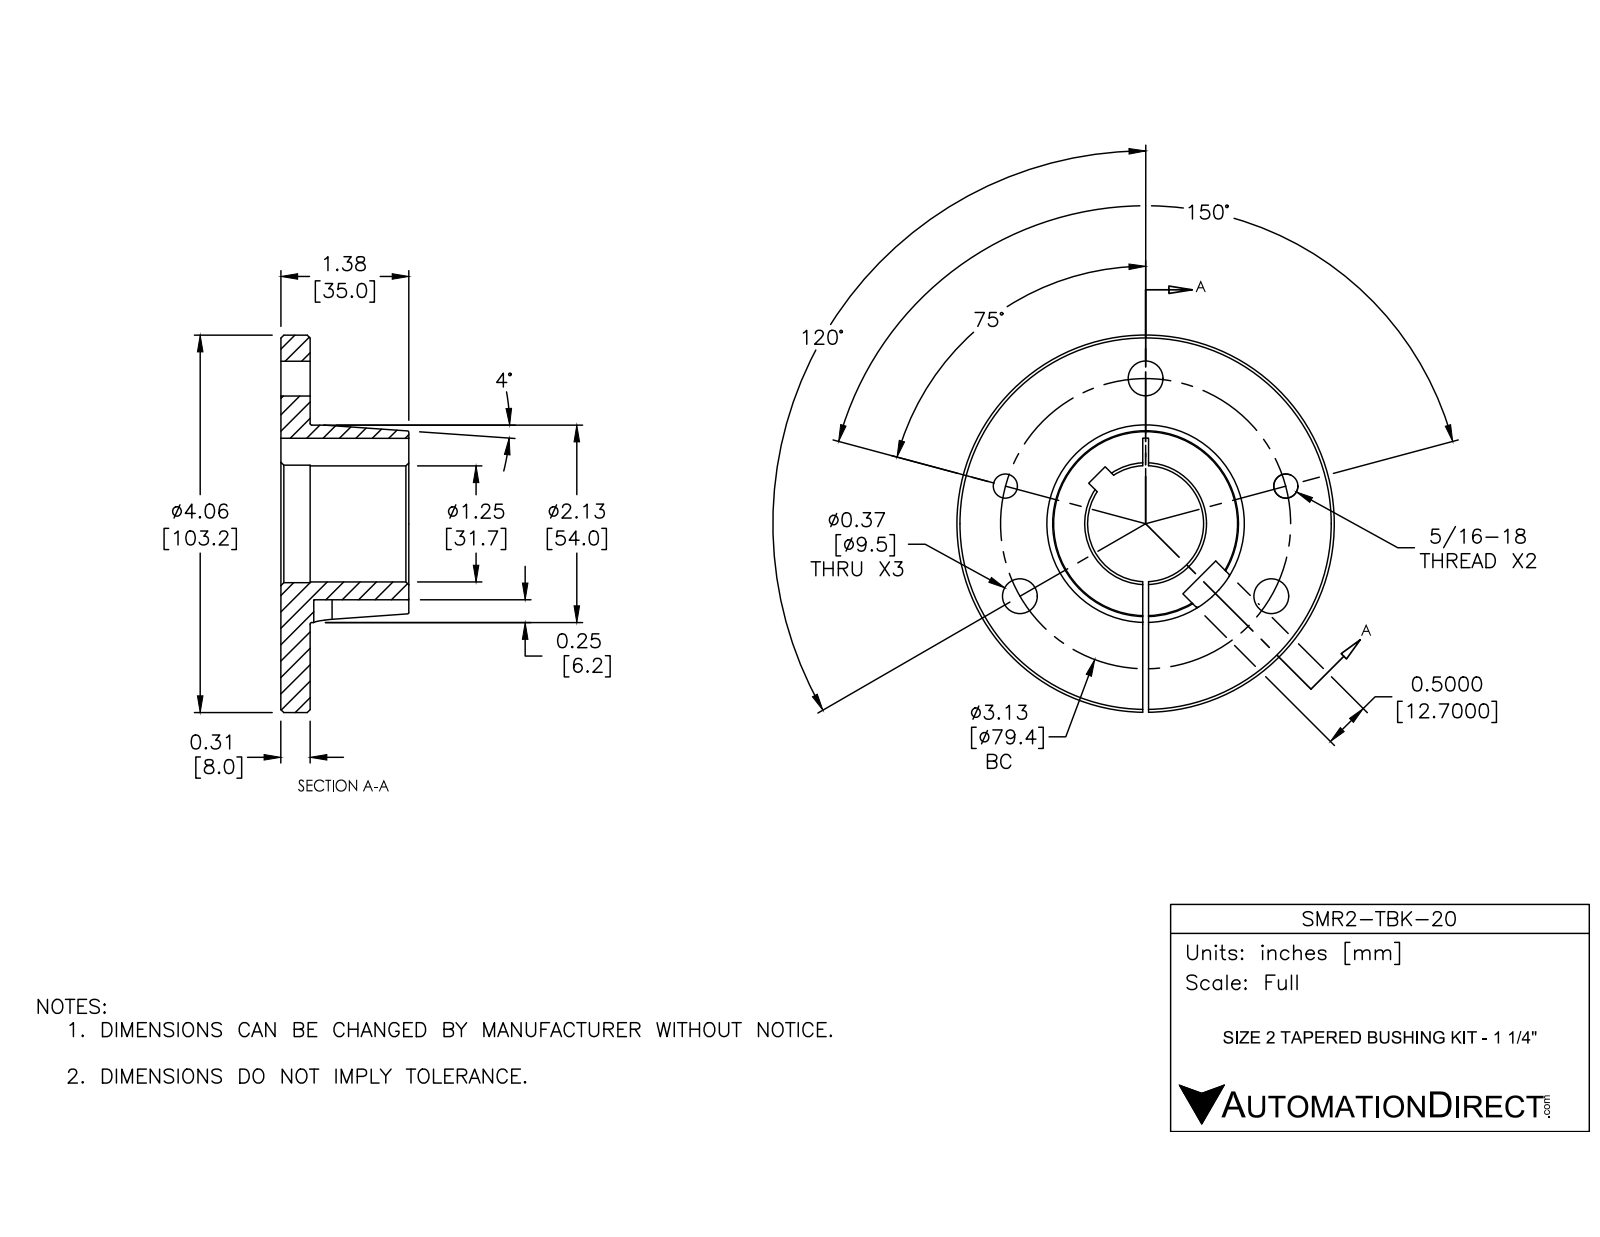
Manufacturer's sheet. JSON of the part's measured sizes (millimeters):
{"part_name": "SMR2-TBK-20", "step_written_by": "SolidWorks 2016 (AUTOMOTIVE_DESIGN)", "units": "millimeters", "bodies": {"solids": 1, "faces": 124, "planar": 18, "cylindrical": 79, "other": 27}, "overall_size": [103.2, 103.2, 35], "volume_mm3": 91490, "surface_area_mm2": 27550, "round_holes": [[9.5, 3], [8.1, 2], [6.6, 1], [31.8, 1], [32.2, 1]], "round_bosses_or_shafts": [[103.2, 1], [54, 1]], "partial_cylinders_radius": [[3.3, 2], [5, 2]], "face_to_face_distances": [8, 35, 27, 1.6, 39.6, 3.2, 9.5, 6.4, 12.7, 9], "hole_center_spacings": [39.7, 68.8, 30.4, 39.7, 39.7, 48.3, 48.4, 76.7]}
